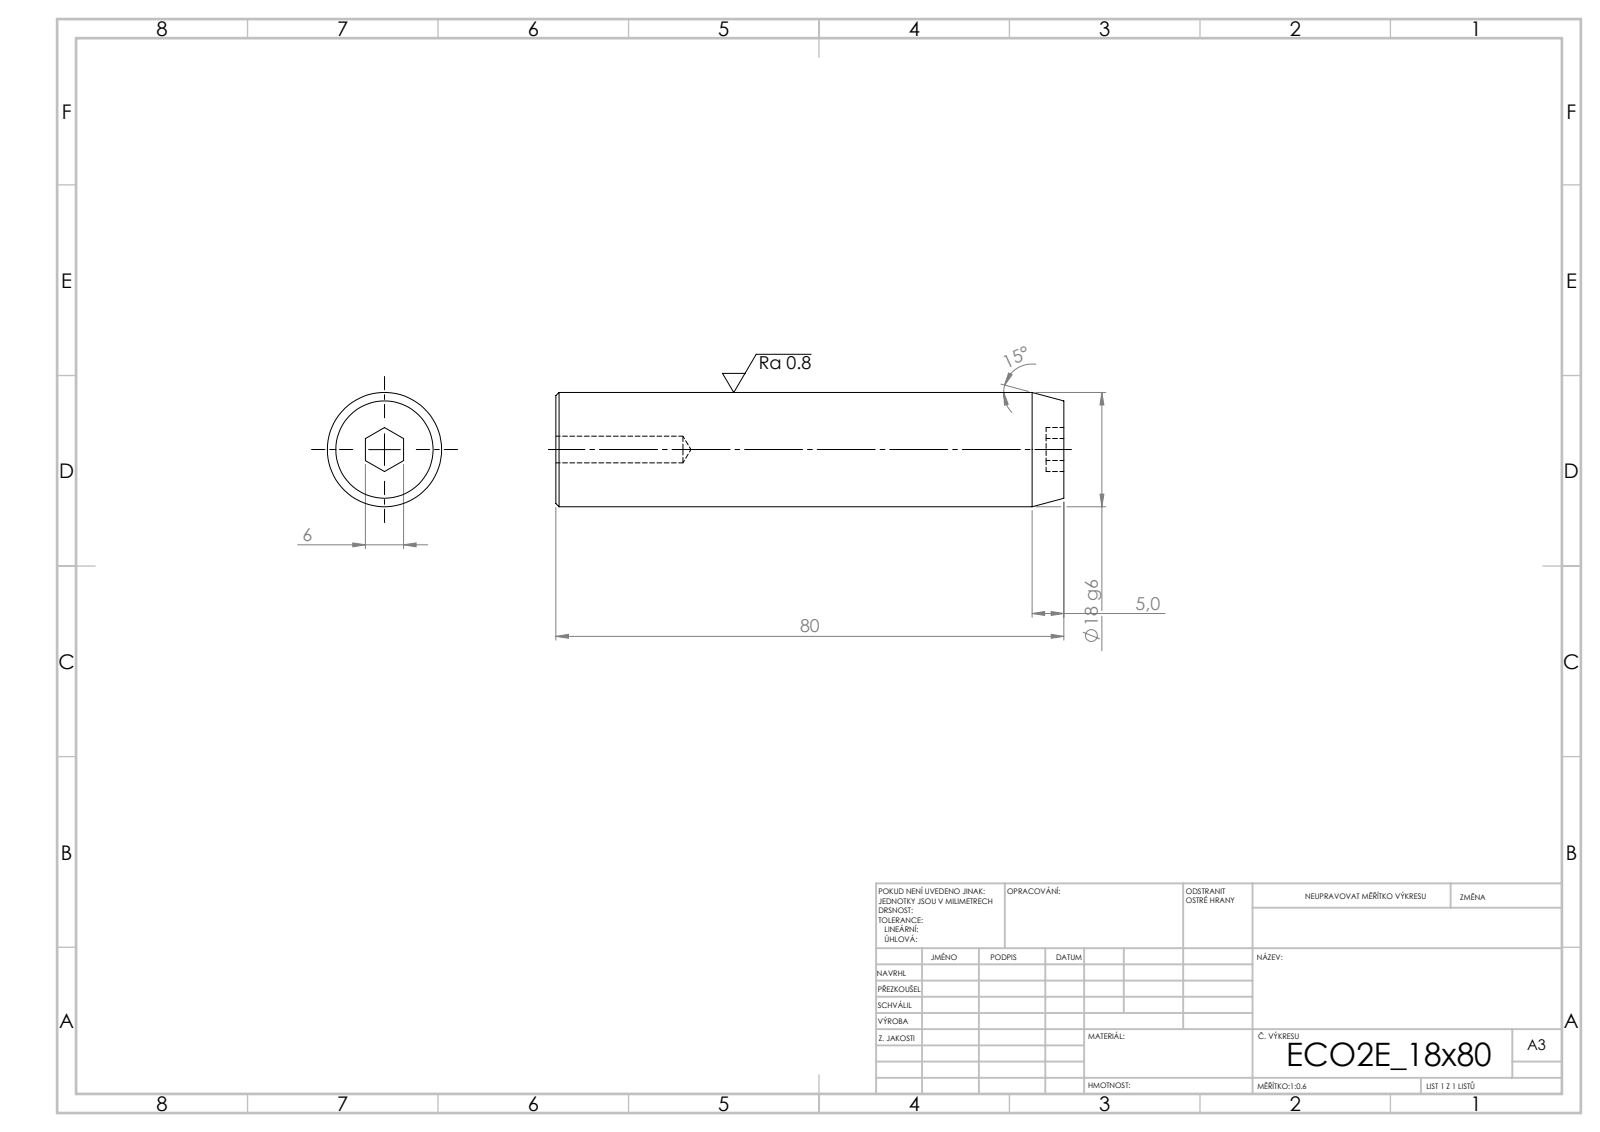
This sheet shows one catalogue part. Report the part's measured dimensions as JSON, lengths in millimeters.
{"step_written_by": "SolidWorks 2019 (CONFIG_CONTROL_DESIGN)", "units": "millimeters", "bodies": {"solids": 1, "faces": 19, "planar": 9, "cylindrical": 4, "other": 6}, "overall_size": [80, 18, 18], "volume_mm3": 19800, "surface_area_mm2": 5258, "round_holes": [[4.2, 1]], "round_bosses_or_shafts": [[18, 1]], "face_to_face_distances": [80, 2.8, 77.2, 6]}
